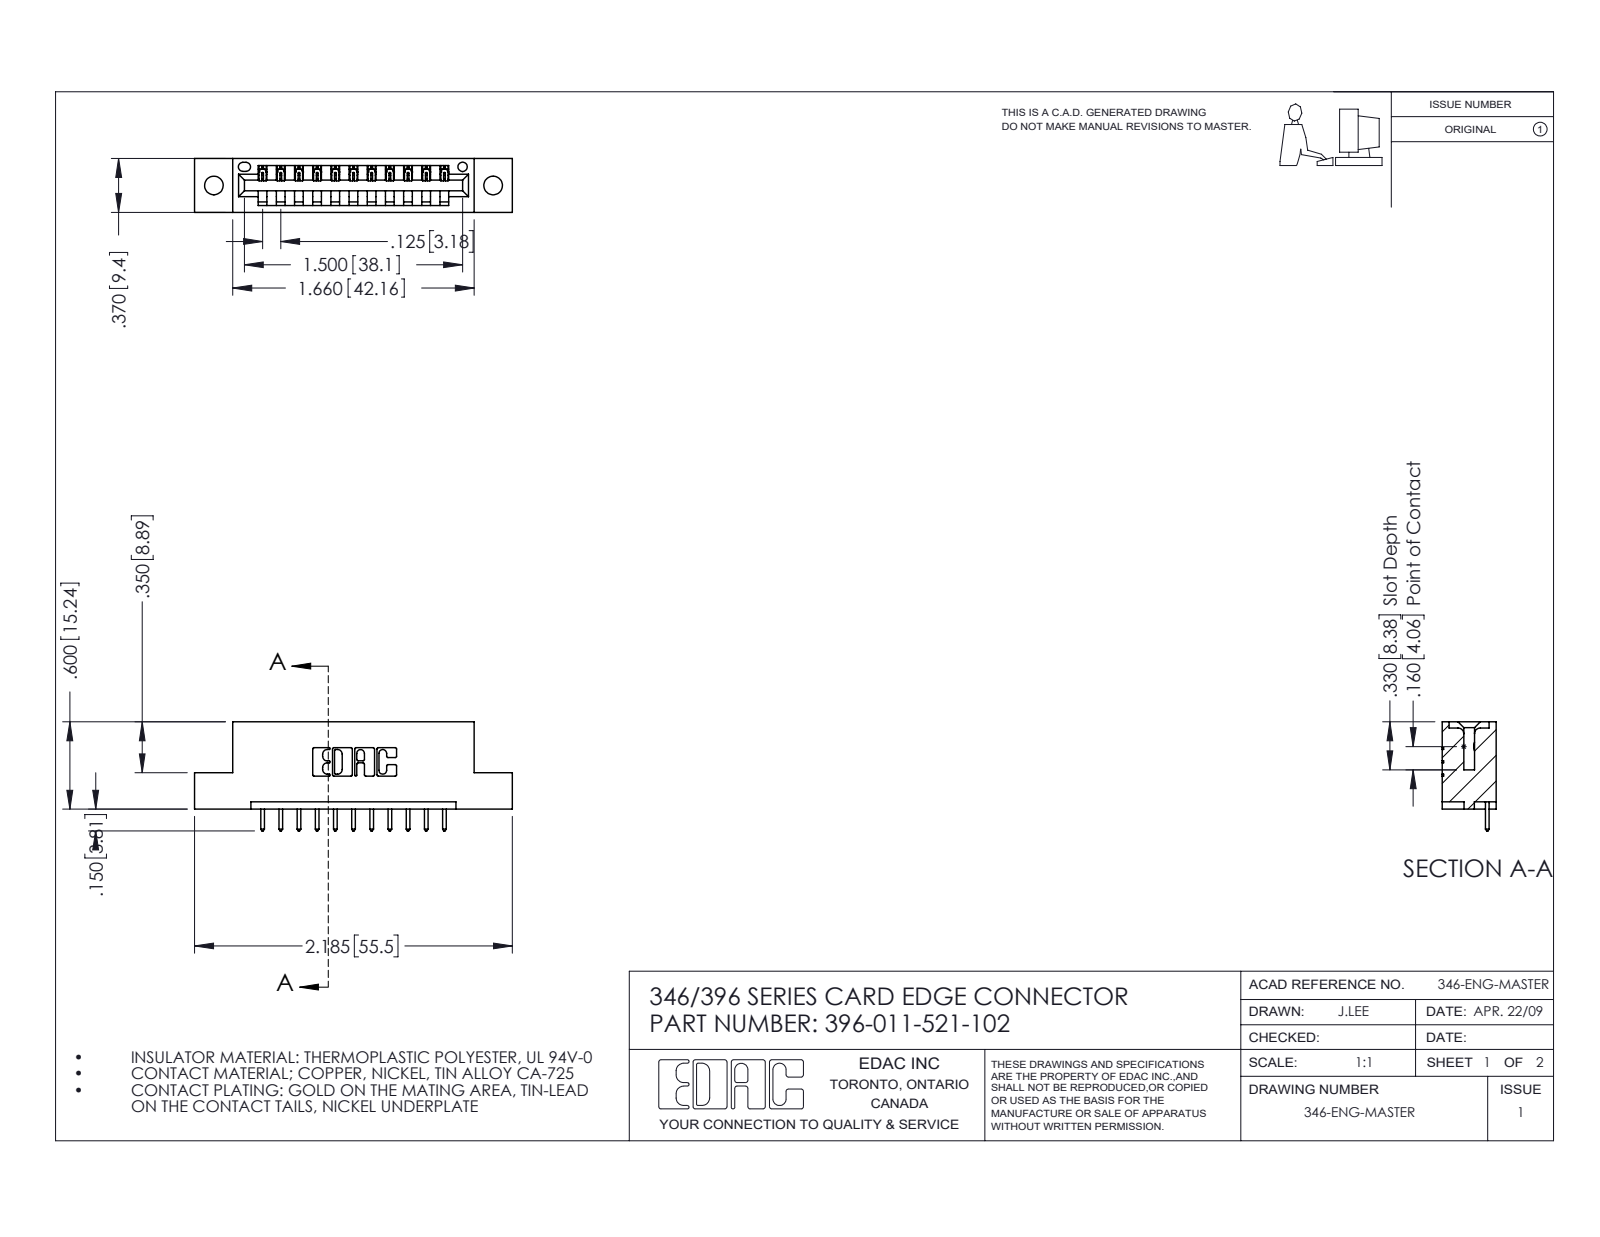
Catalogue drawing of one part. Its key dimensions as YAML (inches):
part_name: "345-292-001_345-293-121; 346 Part_Flush Mounting Lugs - 0.128 Dia; 396-011-521-102"
step_written_by: "SolidWorks 2016 (CONFIG_CONTROL_DESIGN)"
units: inches
bodies: {solids: 12, faces: 760, planar: 516, cylindrical: 244, other: 0}
overall_size: [2.185, 0.75, 0.37]
volume: 0.307
surface_area: 8.615
round_holes:
  - {diameter: 0.128, count: 2}
  - {diameter: 0.064, count: 1}
partial_cylinders:
  - {radius: 0.006, count: 22}
  - {radius: 0.01, count: 22}
  - {radius: 0.01, count: 22}
  - {radius: 0.007, count: 6}
  - {radius: 0.031, count: 6}
  - {radius: 0.026, count: 3}
  - {radius: 0.031, count: 2}
  - {radius: 0.04, count: 2}
face_to_face_distances: [0.25, 0.37, 0.048, 0.322, 0.148, 0.222, 0.1, 0.174, 0.072, 0.298]
hole_center_spacings: [0.246, 1.715, 1.92]
